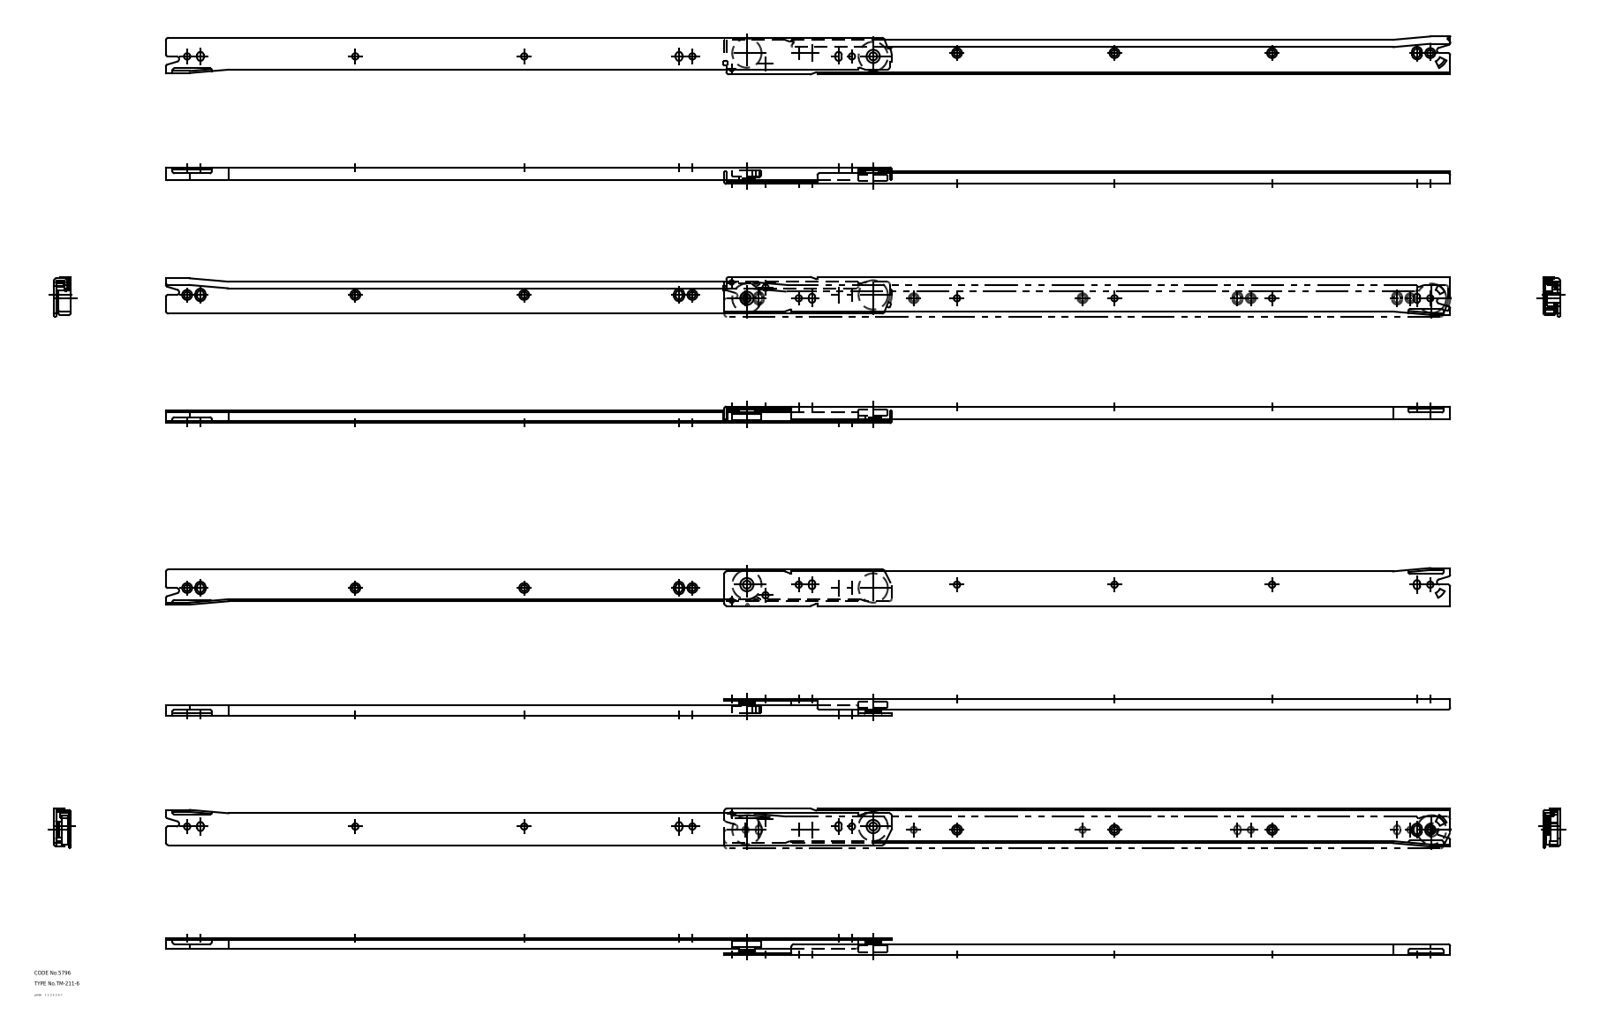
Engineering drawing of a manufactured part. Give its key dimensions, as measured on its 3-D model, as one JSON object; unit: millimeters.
{"part_name": "roller; member_B; member_A; TM_211_6_1305_36", "step_written_by": "CADfix (AUTOMOTIVE_DESIGN)", "units": "millimeters", "bodies": {"solids": 4, "faces": 185, "planar": 0, "cylindrical": 0, "other": 185}, "overall_size": [966, 28.5, 12.5], "volume_mm3": 58120, "surface_area_mm2": 78370}
